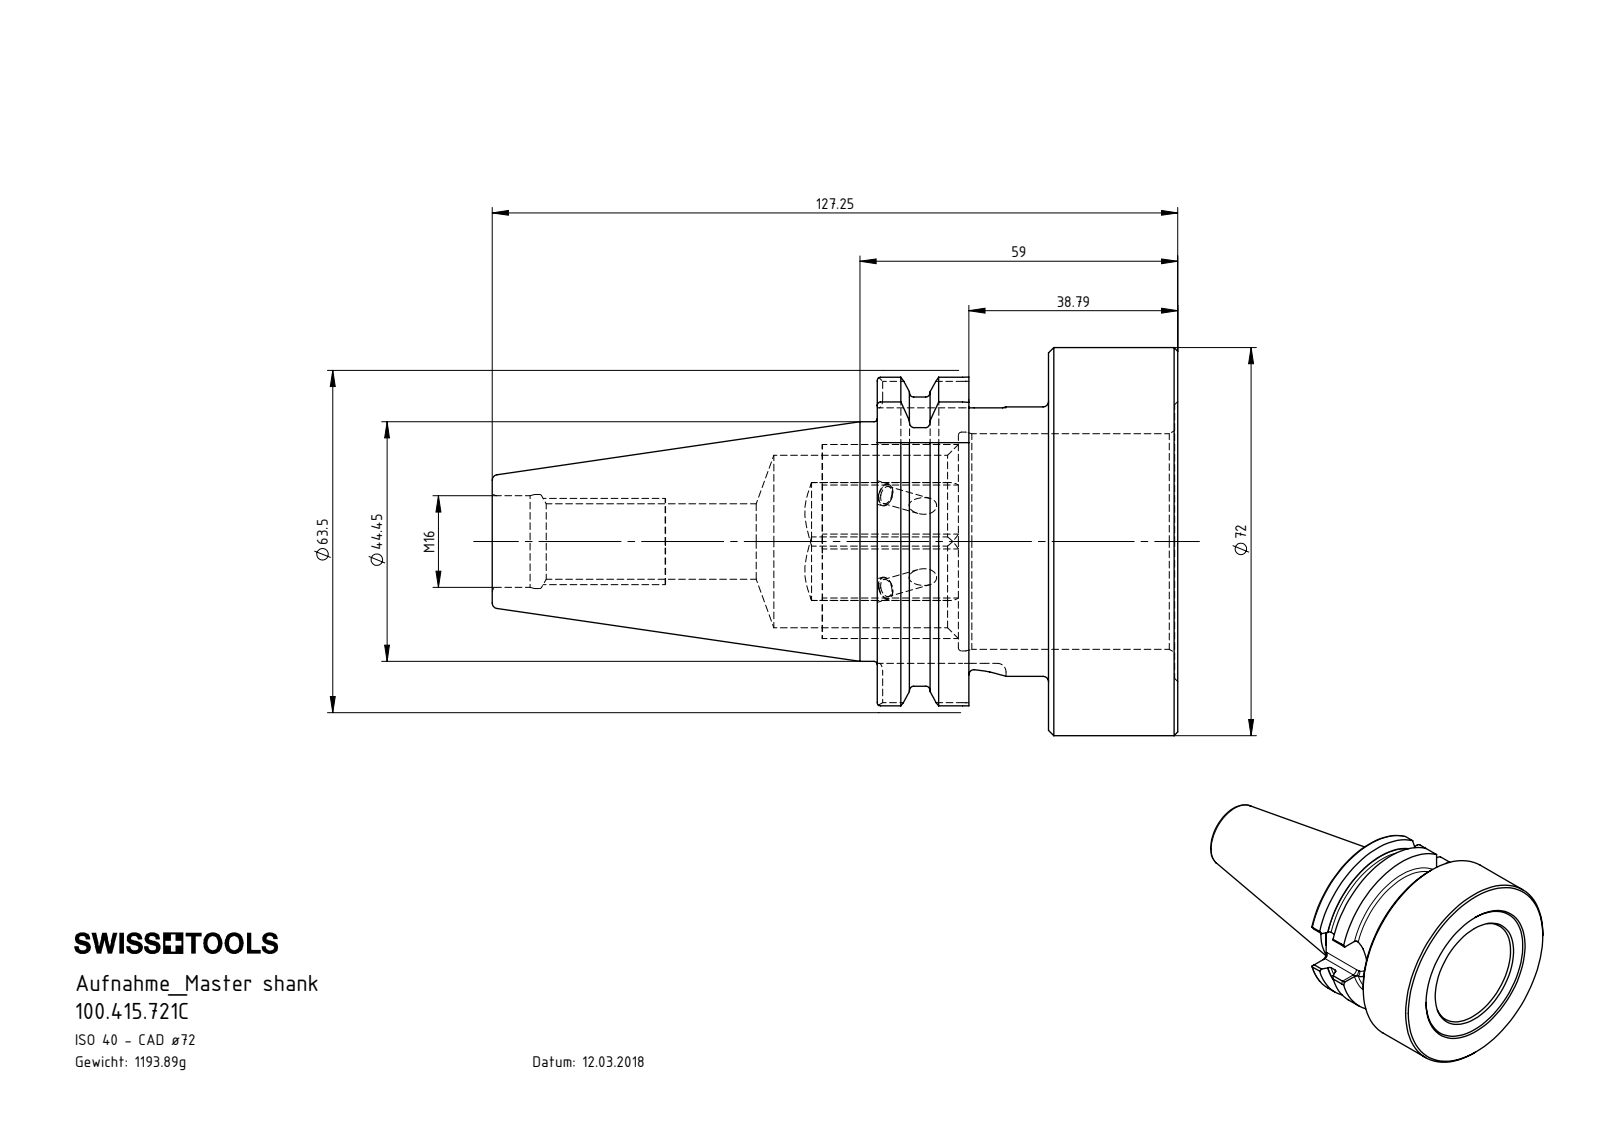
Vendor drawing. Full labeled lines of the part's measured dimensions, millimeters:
Part name (STEP PRODUCT): 100.415.721C
STEP written by: SolidWorks 2017 (CONFIG_CONTROL_DESIGN)
Units: millimetres
Bodies: 1 solid, 163 faces (35 planar, 54 cylindrical, 74 other)
Overall size (bounding box): 127.25 × 72 × 72
Volume: 152 087 mm³ · Surface area: 39 225 mm²
Round holes (diameter × count): ⌀3.3 ×2, ⌀4.2 ×2, ⌀14 ×1, ⌀17 ×1, ⌀17.45 ×1, ⌀32 ×1, ⌀40 ×1, ⌀40.6 ×1
Round bosses / shafts (diameter × count): ⌀72 ×1, ⌀50 ×1, ⌀44.45 ×1
Partial cylindrical surfaces — rounded edges, fillets, slot ends (radius × count): R1.6 ×8, R6.5 ×2, R8 ×1, R8.05 ×1, R28 ×1, R31.75 ×1
Main face-to-face distances: 24, 31.8, 55.8, 17.01, 14.79, 38.79, 55.2, 38.19, 23.4, 0.6
